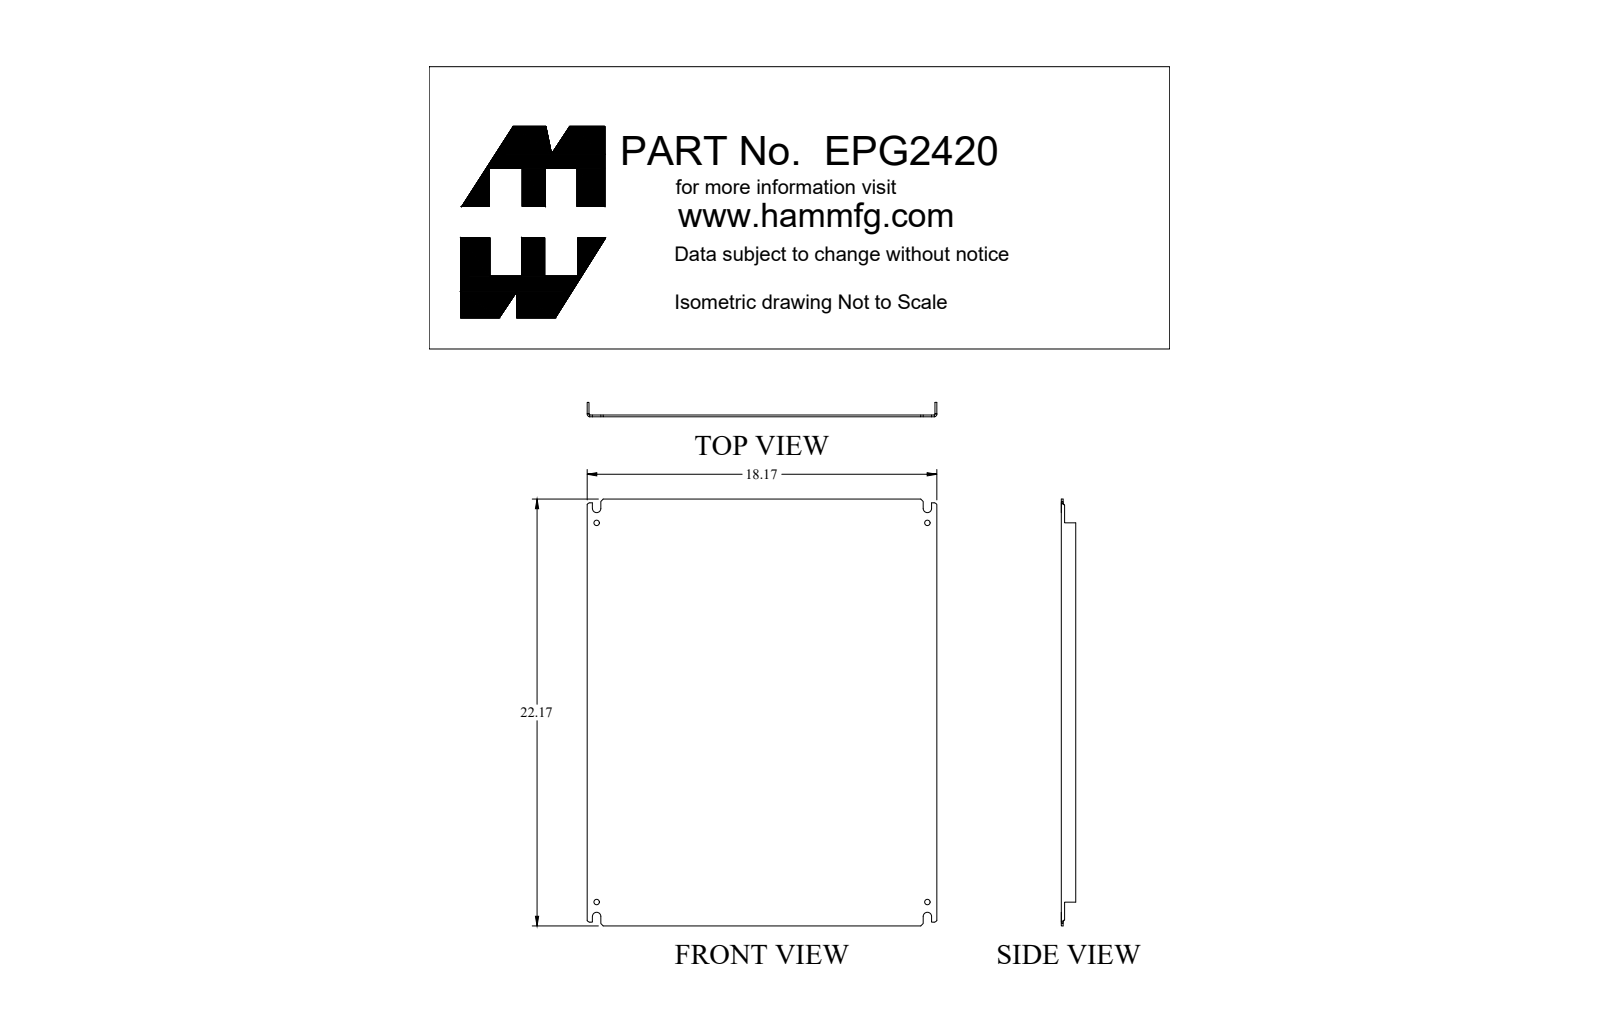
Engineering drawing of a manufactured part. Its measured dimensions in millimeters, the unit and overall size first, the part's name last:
Units: millimetres
Overall size (bounding box): 563.1 × 461.5 × 19.1
Round holes (diameter × count): ⌀7.1 ×4
Partial cylindrical surfaces — rounded edges, fillets, slot ends (radius × count): R5.6 ×4, R1.2 ×2, R1.6 ×2, R3.6 ×2
Main face-to-face distances: 2.4, 459.1, 456.7, 461.5, 19.1, 16.6, 563.1, 4.3, 1.9, 14.7
Hole centre spacings: 436.6, 500.1, 663.8
Volume: 662 200 mm³ · Surface area: 554 400 mm²
Bodies: 1 solid, 84 faces (50 planar, 26 cylindrical, 8 other)
Part name (STEP PRODUCT): EPG2420
STEP written by: SolidWorks 2018 (AUTOMOTIVE_DESIGN)
